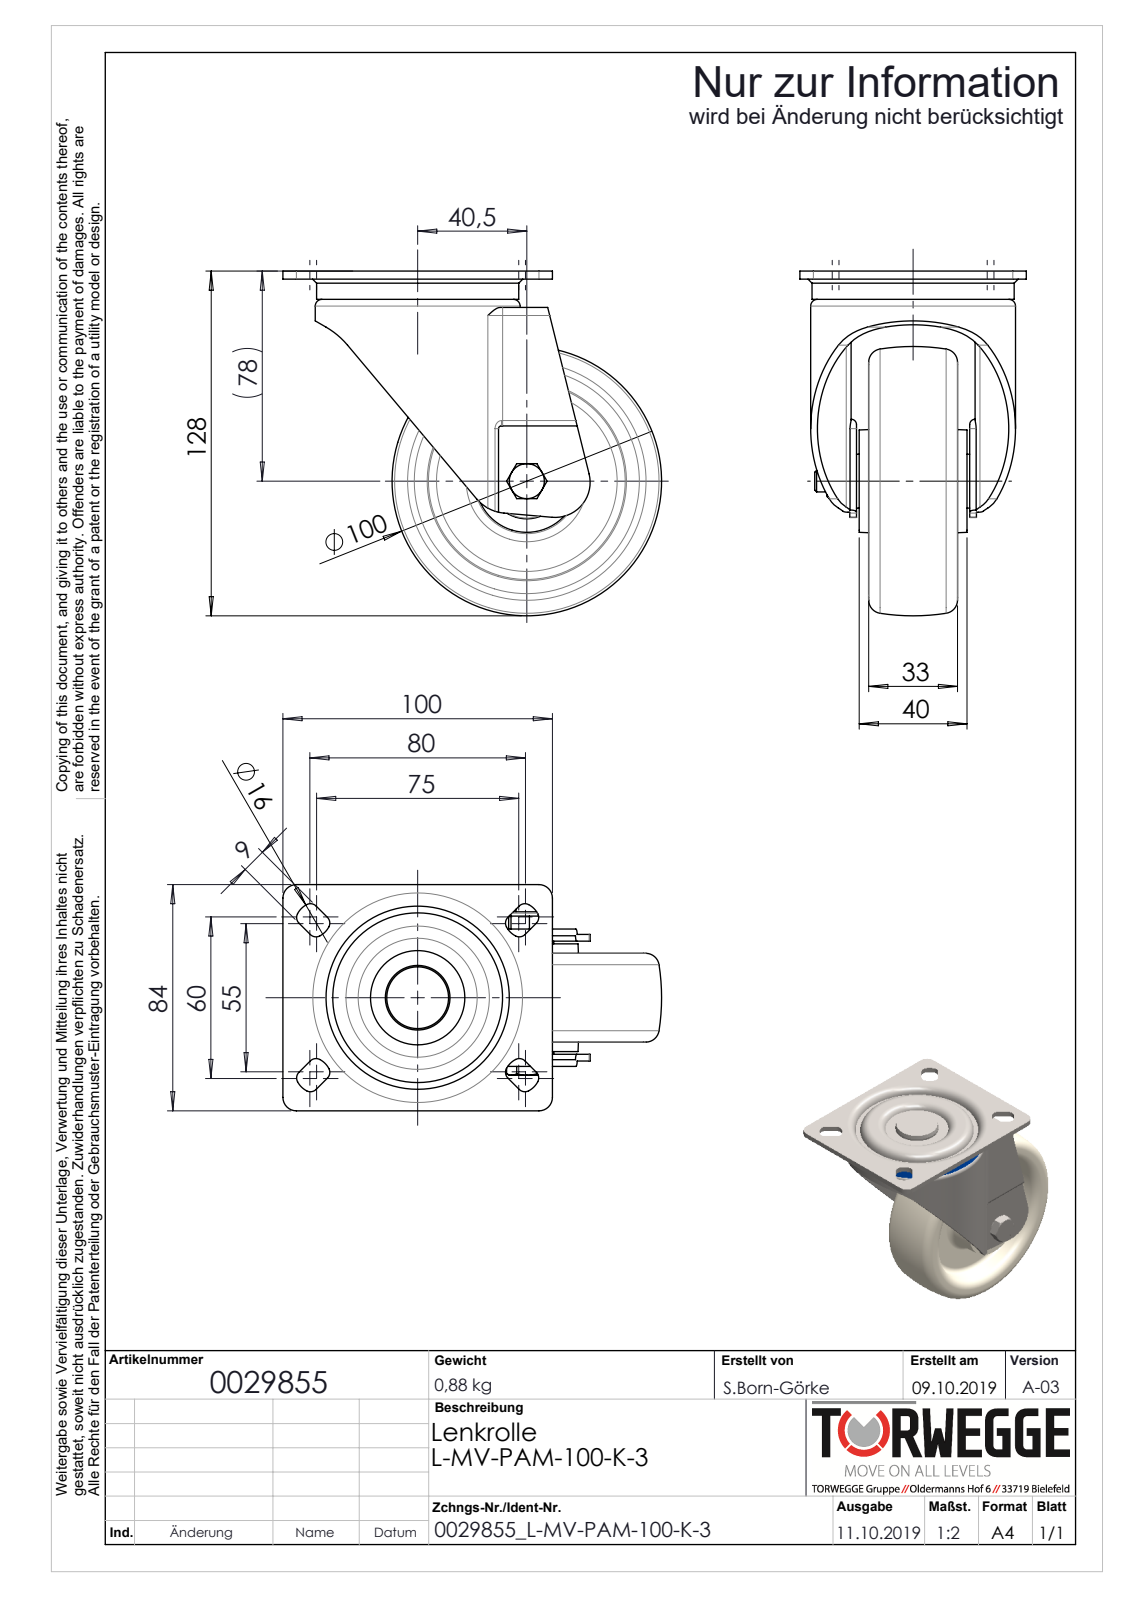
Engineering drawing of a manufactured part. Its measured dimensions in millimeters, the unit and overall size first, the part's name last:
Units: millimetres
Overall size (bounding box): 140.5 × 128 × 84
Round holes (diameter × count): ⌀6.8 ×1, ⌀8 ×1, ⌀8.2 ×1, ⌀8.5 ×1, ⌀12 ×1, ⌀23 ×1, ⌀23.2 ×1
Round bosses / shafts (diameter × count): ⌀76 ×1, ⌀75 ×1, ⌀28 ×1, ⌀24 ×1, ⌀20 ×1, ⌀16.8 ×1, ⌀13 ×1, ⌀11.9 ×1
Partial cylindrical surfaces — rounded edges, fillets, slot ends (radius × count): R3 ×18, R2 ×10, R7.97 ×8, R5 ×4, R6 ×2, R8 ×2, R1 ×1, R13 ×1
Main face-to-face distances: 3, 10, 2.5, 13, 2, 46.5, 0.5, 18.5, 16, 44.5
Volume: 273 187 mm³ · Surface area: 90 885 mm²
Bodies: 8 solids, 350 faces (91 planar, 132 cylindrical, 127 other)
Part name (STEP PRODUCT): 0029855_L-MV-PAM-100-K-3_(A-03)
STEP written by: SolidWorks 2018 (AUTOMOTIVE_DESIGN)
